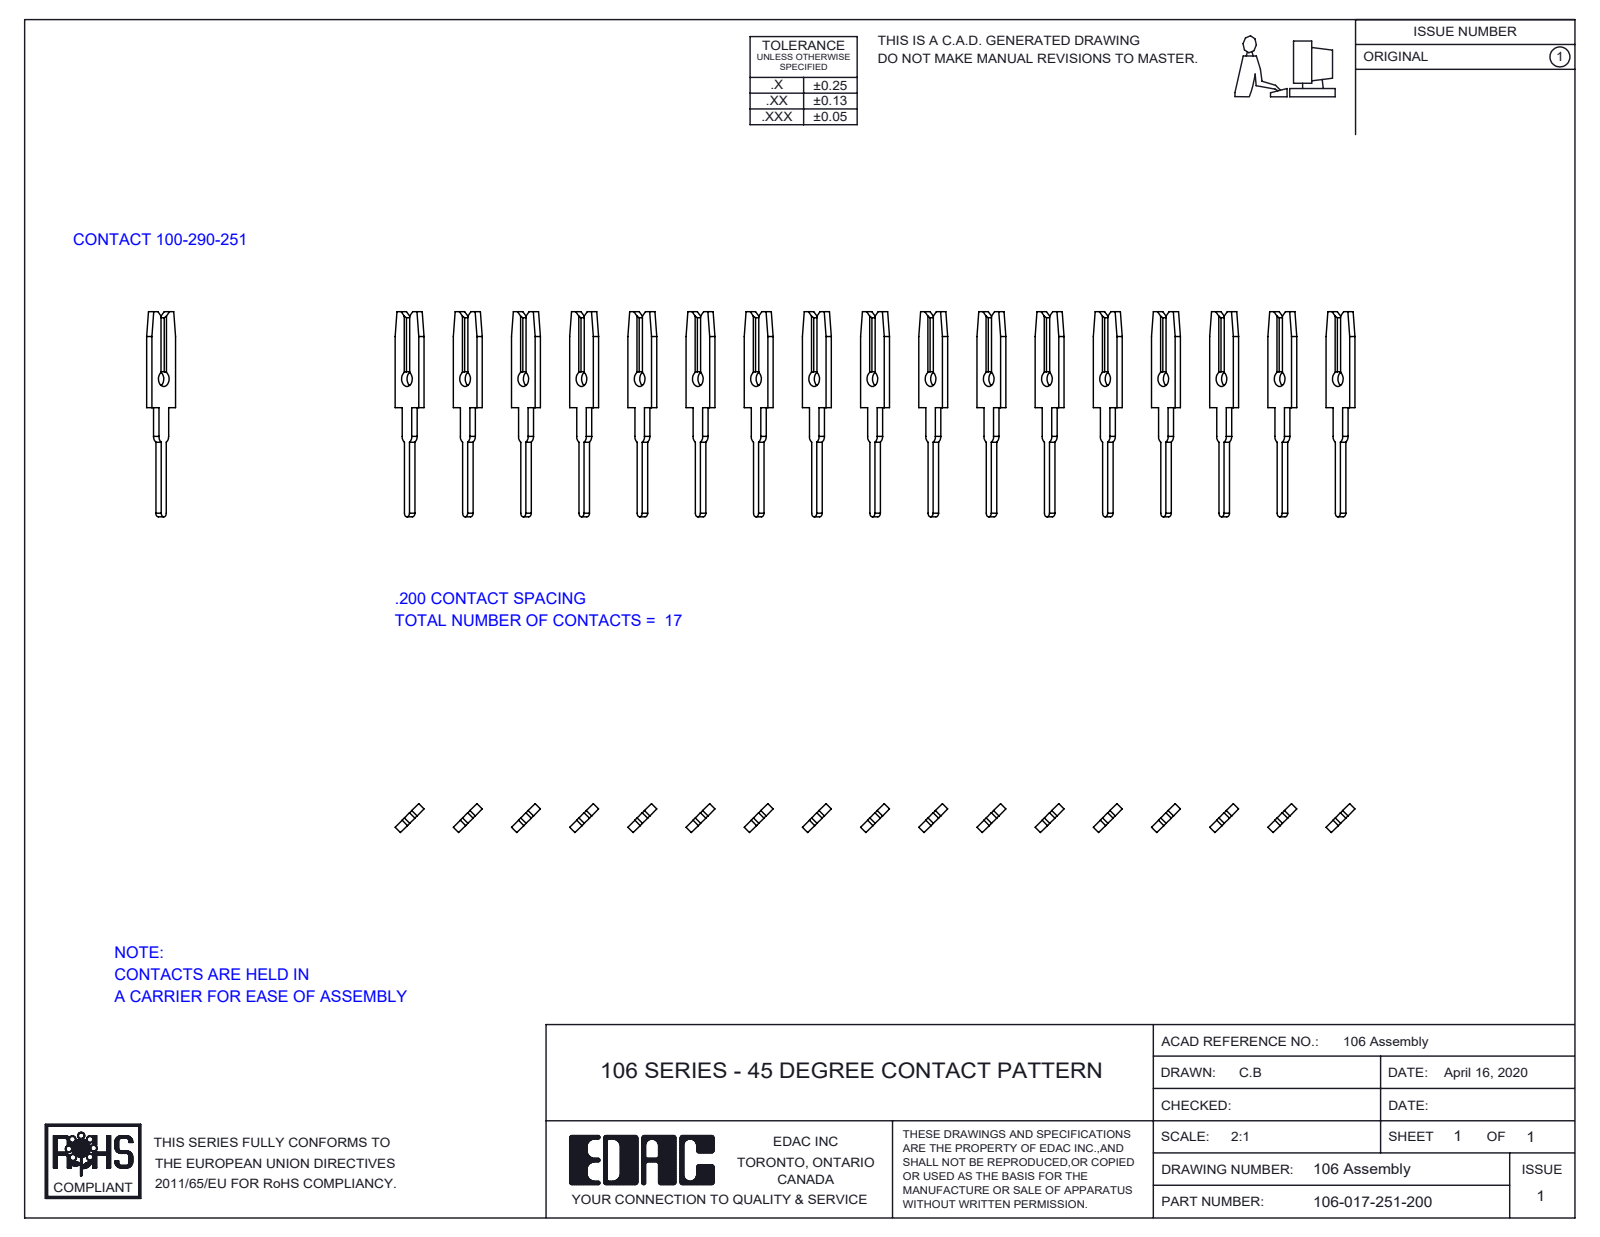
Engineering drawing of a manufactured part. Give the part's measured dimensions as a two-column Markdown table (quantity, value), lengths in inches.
| quantity | value |
| --- | --- |
| part name | 106-017-251-200; 100-290-001_100-290-251 |
| STEP written by | SolidWorks 2016 (CONFIG_CONTROL_DESIGN) |
| units | inches |
| bodies | 17 solids, 476 faces (374 planar, 102 cylindrical, 0 other) |
| overall size | 3.3 × 0.705 × 0.1 |
| volume | 0.019 in³ |
| surface area | 2.368 in² |
| round holes (diameter × count) | 0.052 × 17 |
| partial cylindrical surfaces (radius × count) | 0.012 × 17, 0.024 × 17 |
| main face-to-face distances | 0.141, 0.283, 0.848, 0.707, 0.99, 0.566, 0.424, 1.131, 0.424, 1.272 |
| hole center spacings | 0.141, 0.283, 0.424, 0.848, 0.99, 0.566, 0.707, 1.131 |
